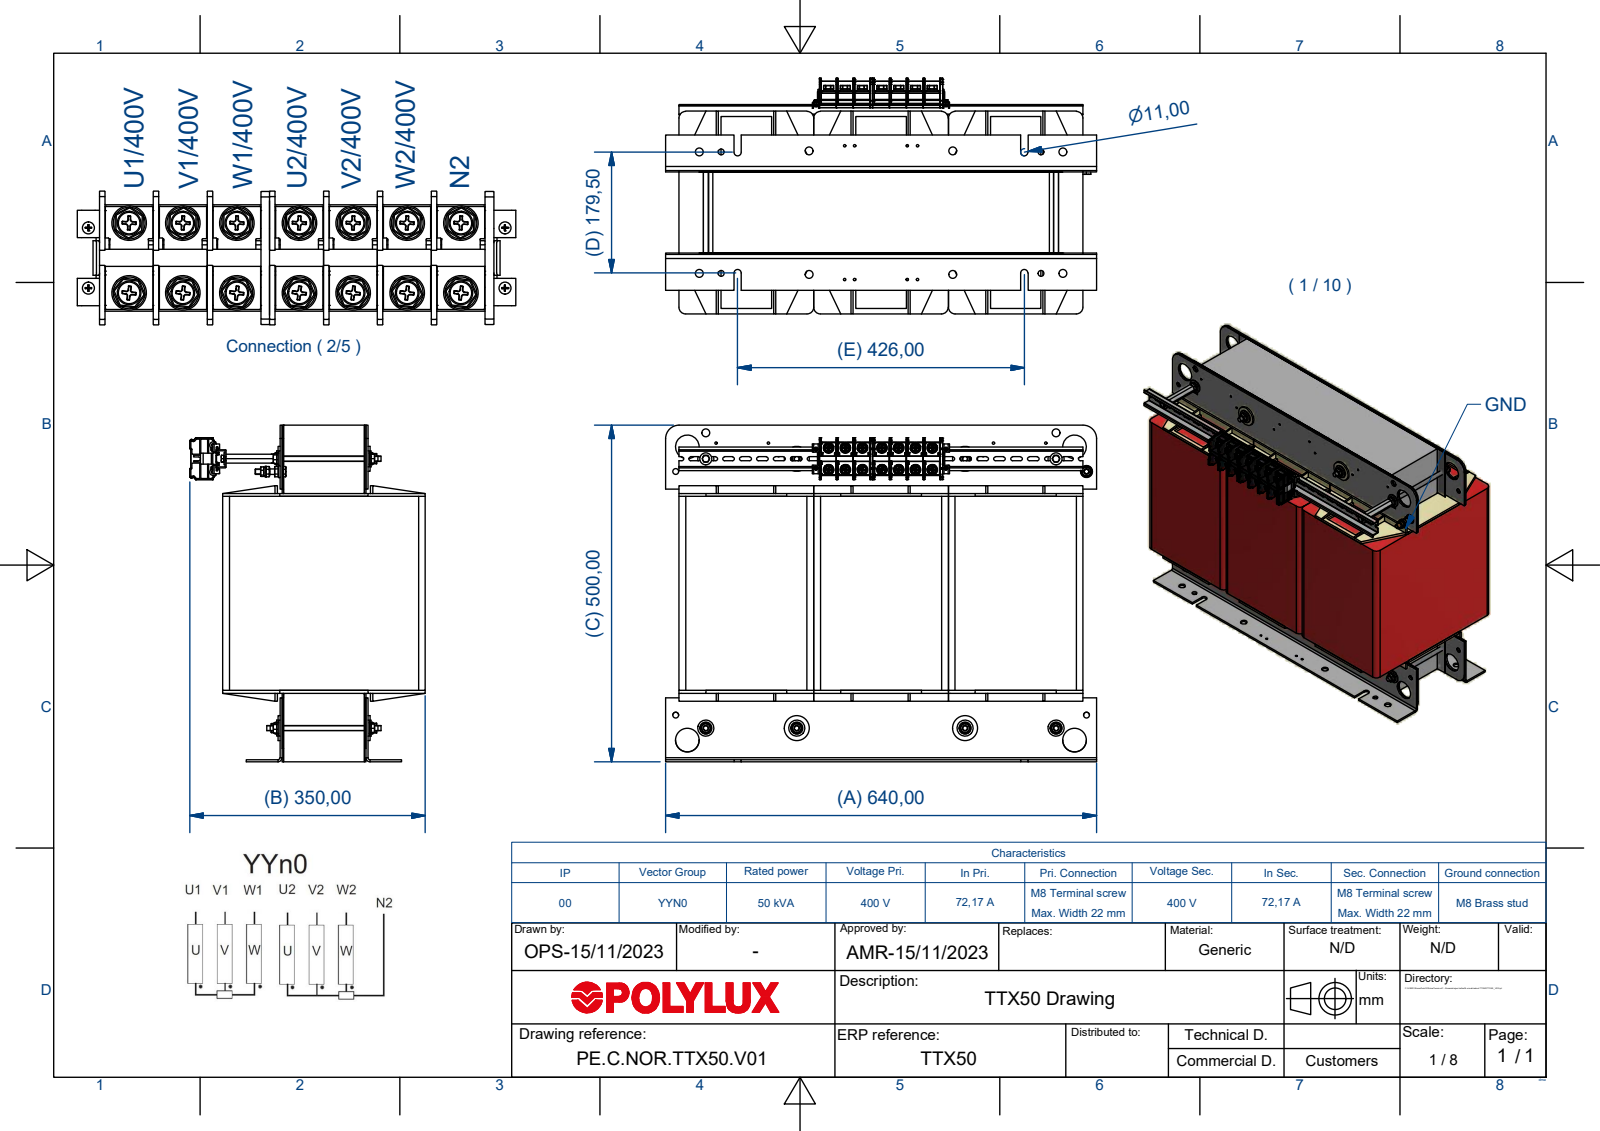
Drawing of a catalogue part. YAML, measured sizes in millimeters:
part_name: "TTX50_V02"
step_written_by: "Autodesk Inventor 2018 (AUTOMOTIVE_DESIGN)"
units: millimeters
bodies: {solids: 148, faces: 8621, planar: 3071, cylindrical: 3263, other: 2287}
overall_size: [640, 500, 339.6]
volume: 66810000
surface_area: 5285000
round_holes:
  - {diameter: 8.4, count: 23}
  - {diameter: 8.5, count: 23}
  - {diameter: 12, count: 22}
  - {diameter: 4.5, count: 20}
  - {diameter: 3.5, count: 18}
  - {diameter: 8, count: 14}
  - {diameter: 10, count: 14}
  - {diameter: 9, count: 10}
  - {diameter: 11.5, count: 10}
  - {diameter: 6.65, count: 9}
  - {diameter: 35, count: 6}
  - {diameter: 11.25, count: 4}
round_bosses_or_shafts:
  - {diameter: 16, count: 23}
  - {diameter: 14.8, count: 22}
  - {diameter: 10.1, count: 14}
  - {diameter: 7.85, count: 14}
  - {diameter: 8, count: 9}
  - {diameter: 3.92, count: 4}
  - {diameter: 3, count: 4}
  - {diameter: 8.88, count: 2}
partial_cylinders:
  - {radius: 0.15, count: 1173}
  - {radius: 0.5, count: 120}
  - {radius: 1, count: 74}
  - {radius: 0.35, count: 56}
  - {radius: 3, count: 50}
  - {radius: 1.55, count: 44}
  - {radius: 5, count: 20}
  - {radius: 0.25, count: 14}
face_to_face_distances: [200, 4, 2, 122, 400, 150, 50, 46, 154, 104]
hole_center_spacings: [333.54, 206, 78, 94.82, 250, 422.17, 15, 23.82]
